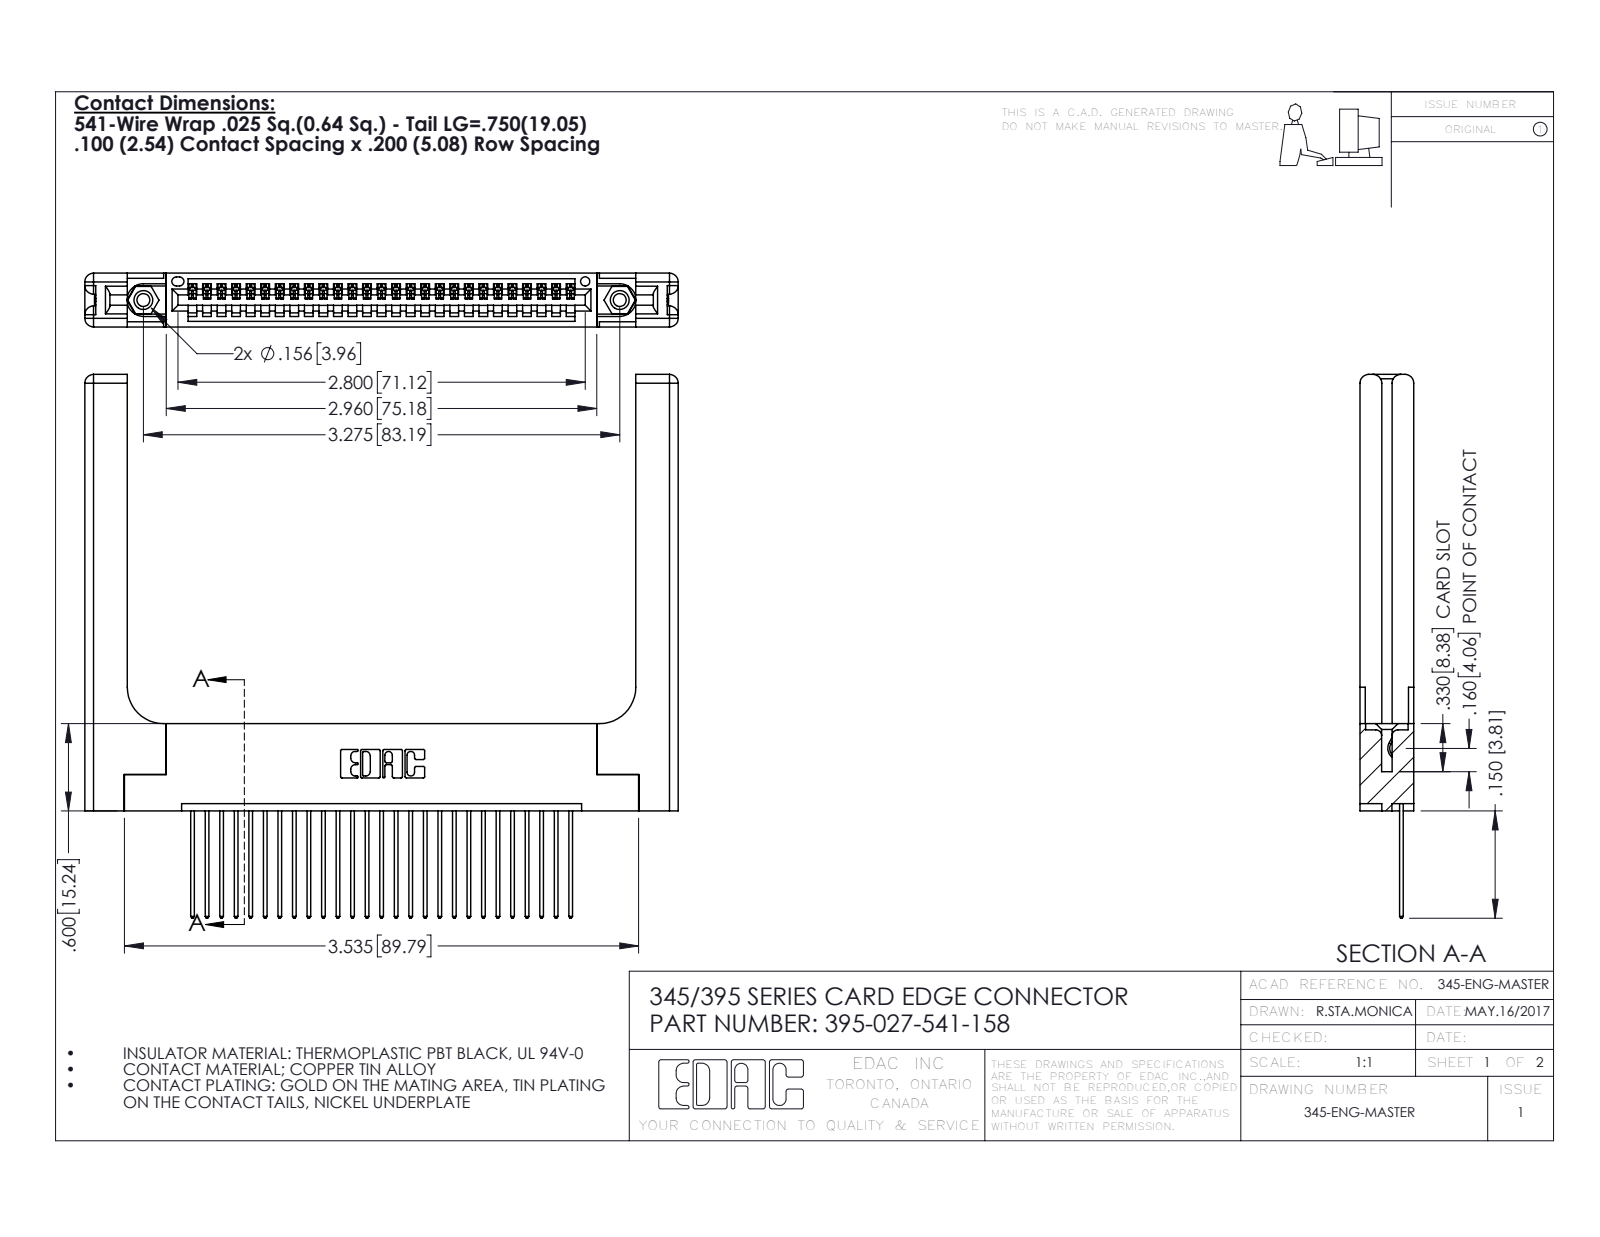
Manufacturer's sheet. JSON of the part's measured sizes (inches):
{"part_name": "345-220-058_345-220-058; 345-250-001_345-250-001-102; 345-292-001_345-293-141; 345 Part_Flush Mounting Lugs - 0.156 Dia-TH (+1 more)", "step_written_by": "SolidWorks 2016 (CONFIG_CONTROL_DESIGN)", "units": "inches", "bodies": {"solids": 32, "faces": 1948, "planar": 1308, "cylindrical": 580, "other": 60}, "overall_size": [4.079, 3.737, 0.37], "volume_in3": 1.117, "surface_area_in2": 28.92, "round_holes": [[0.089, 2], [0.125, 2], [0.156, 2], [0.064, 1]], "round_bosses_or_shafts": [[0.155, 2]], "partial_cylinders_radius": [[0.006, 54], [0.01, 54], [0.01, 22], [0.06, 16], [0.007, 6], [0.031, 6], [0.026, 3], [0.03, 2]], "face_to_face_distances": [0.37, 0.072, 0.298, 0.2, 0.098, 0.272, 0.025, 0.148, 0.15, 0.077], "hole_center_spacings": [0.27, 3.04, 3.275]}
